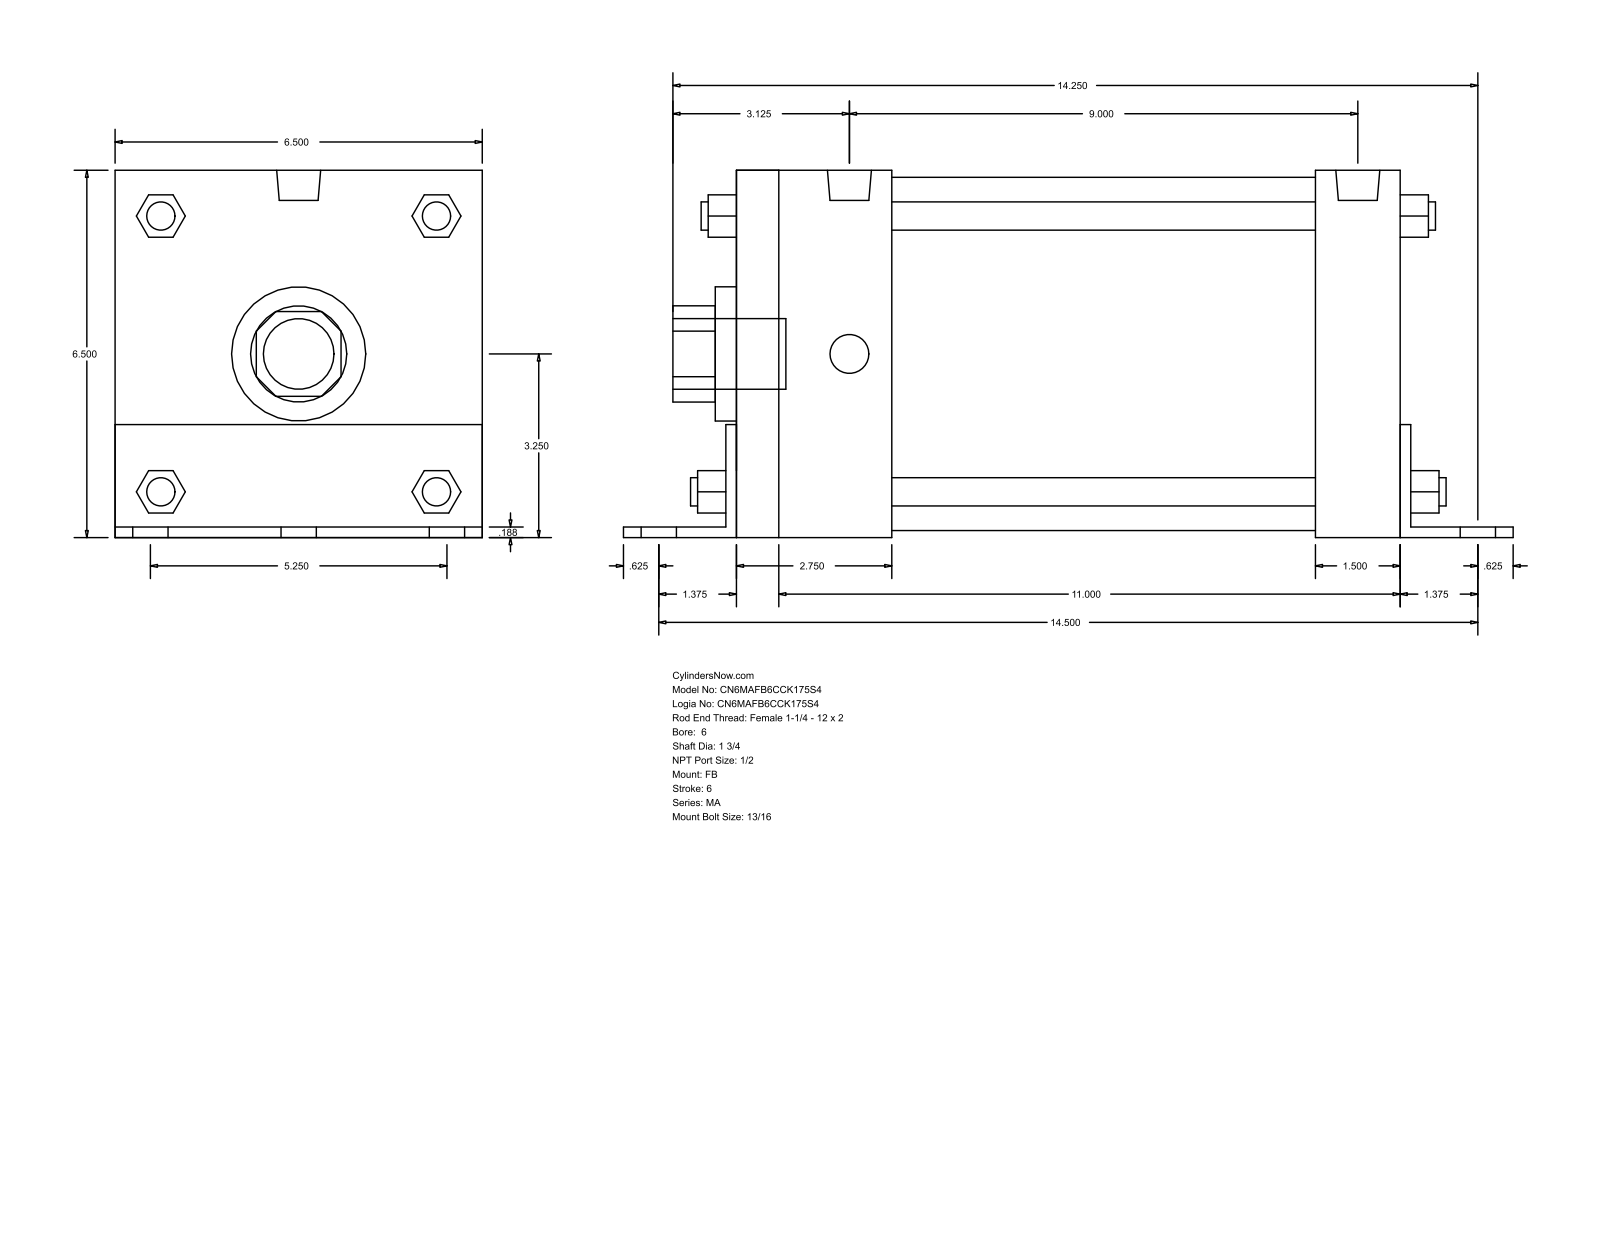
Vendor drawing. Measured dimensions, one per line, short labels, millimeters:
name: MA_FB__0600_1.75
written by: GSSL Pune (CONFIG_CONTROL_DESIGN)
unit: mm
bodies: 0 solids, 140 faces (105 planar, 35 cylindrical, 0 other)
size: 400.05 × 165.15 × 165.1
holes: 1× ⌀44.45, 1× ⌀60.33, 1× ⌀158.75
bosses: 6× ⌀20.64, 4× ⌀17.46, 4× ⌀12.7, 2× ⌀19.77, 1× ⌀31.75
rounds: 1× R21.63, 1× R32.05
face distances: 165.1, 4.76, 298.45, 165.15, 4.71, 160.39, 4.77, 38.09, 42.86, 303.22
